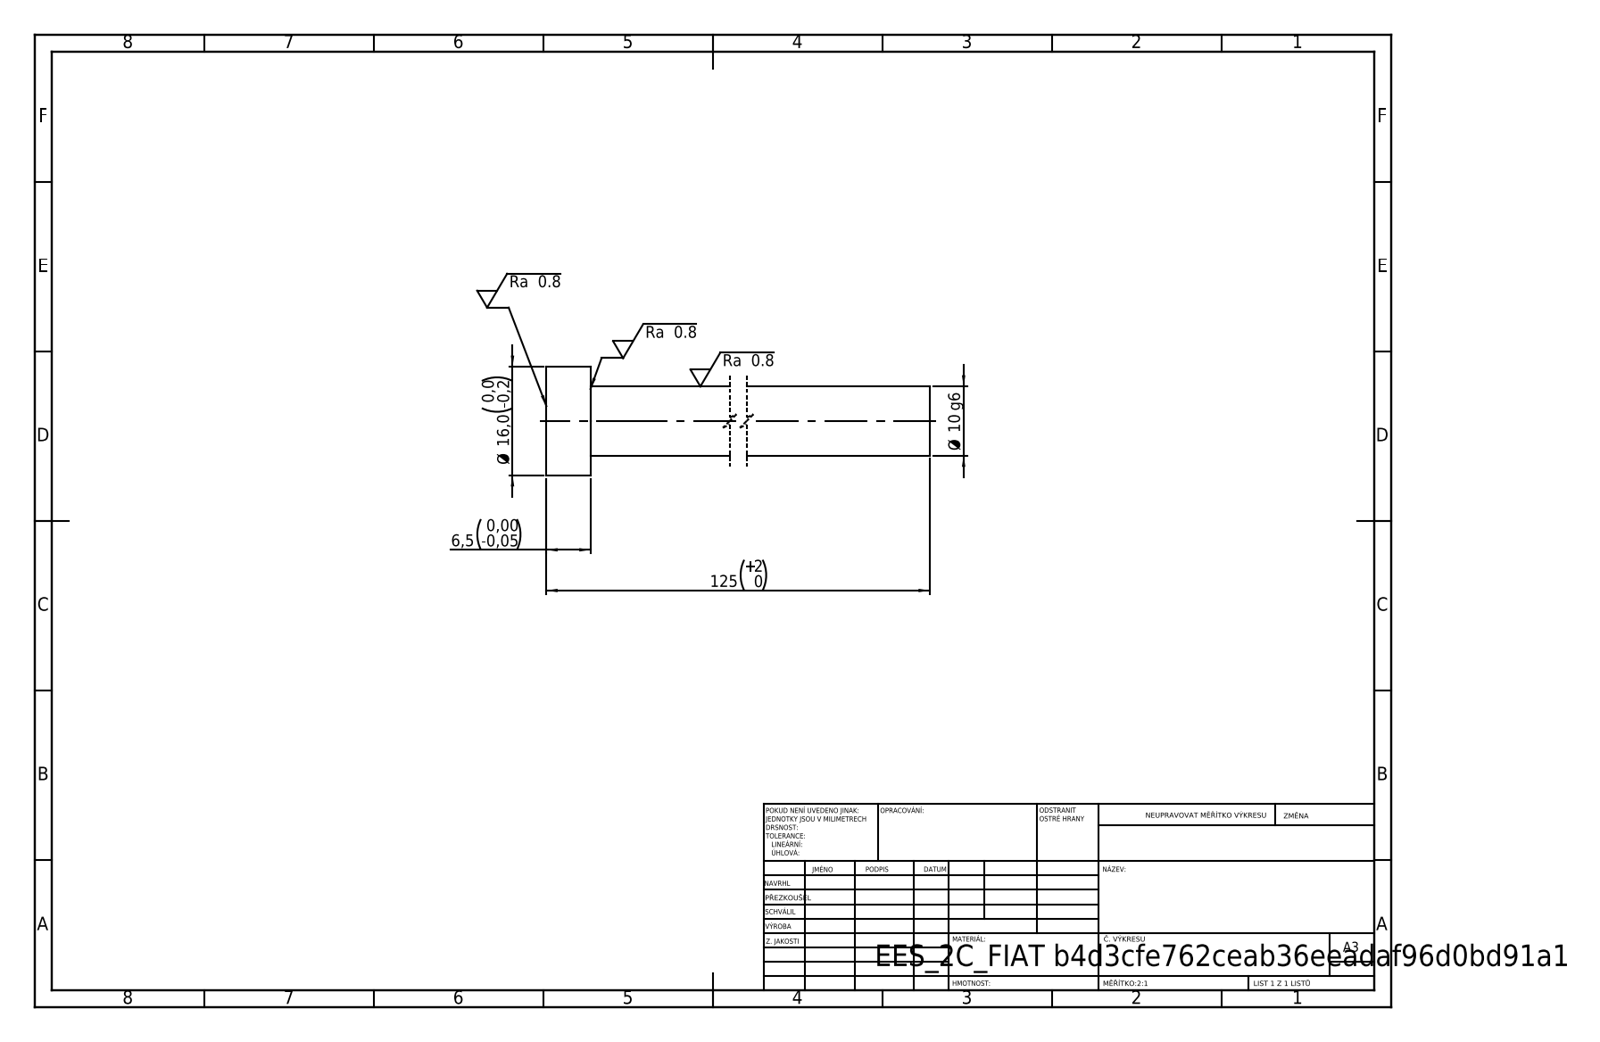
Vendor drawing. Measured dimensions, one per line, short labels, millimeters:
written by: SolidWorks 2019 (CONFIG_CONTROL_DESIGN)
unit: mm
bodies: 1 solid, 7 faces (3 planar, 4 cylindrical, 0 other)
size: 125 × 16 × 16
volume: 10 990 mm³; area: 4 526 mm²
bosses: 1× ⌀16, 1× ⌀10.2
face distances: 6.5, 125, 118.5
